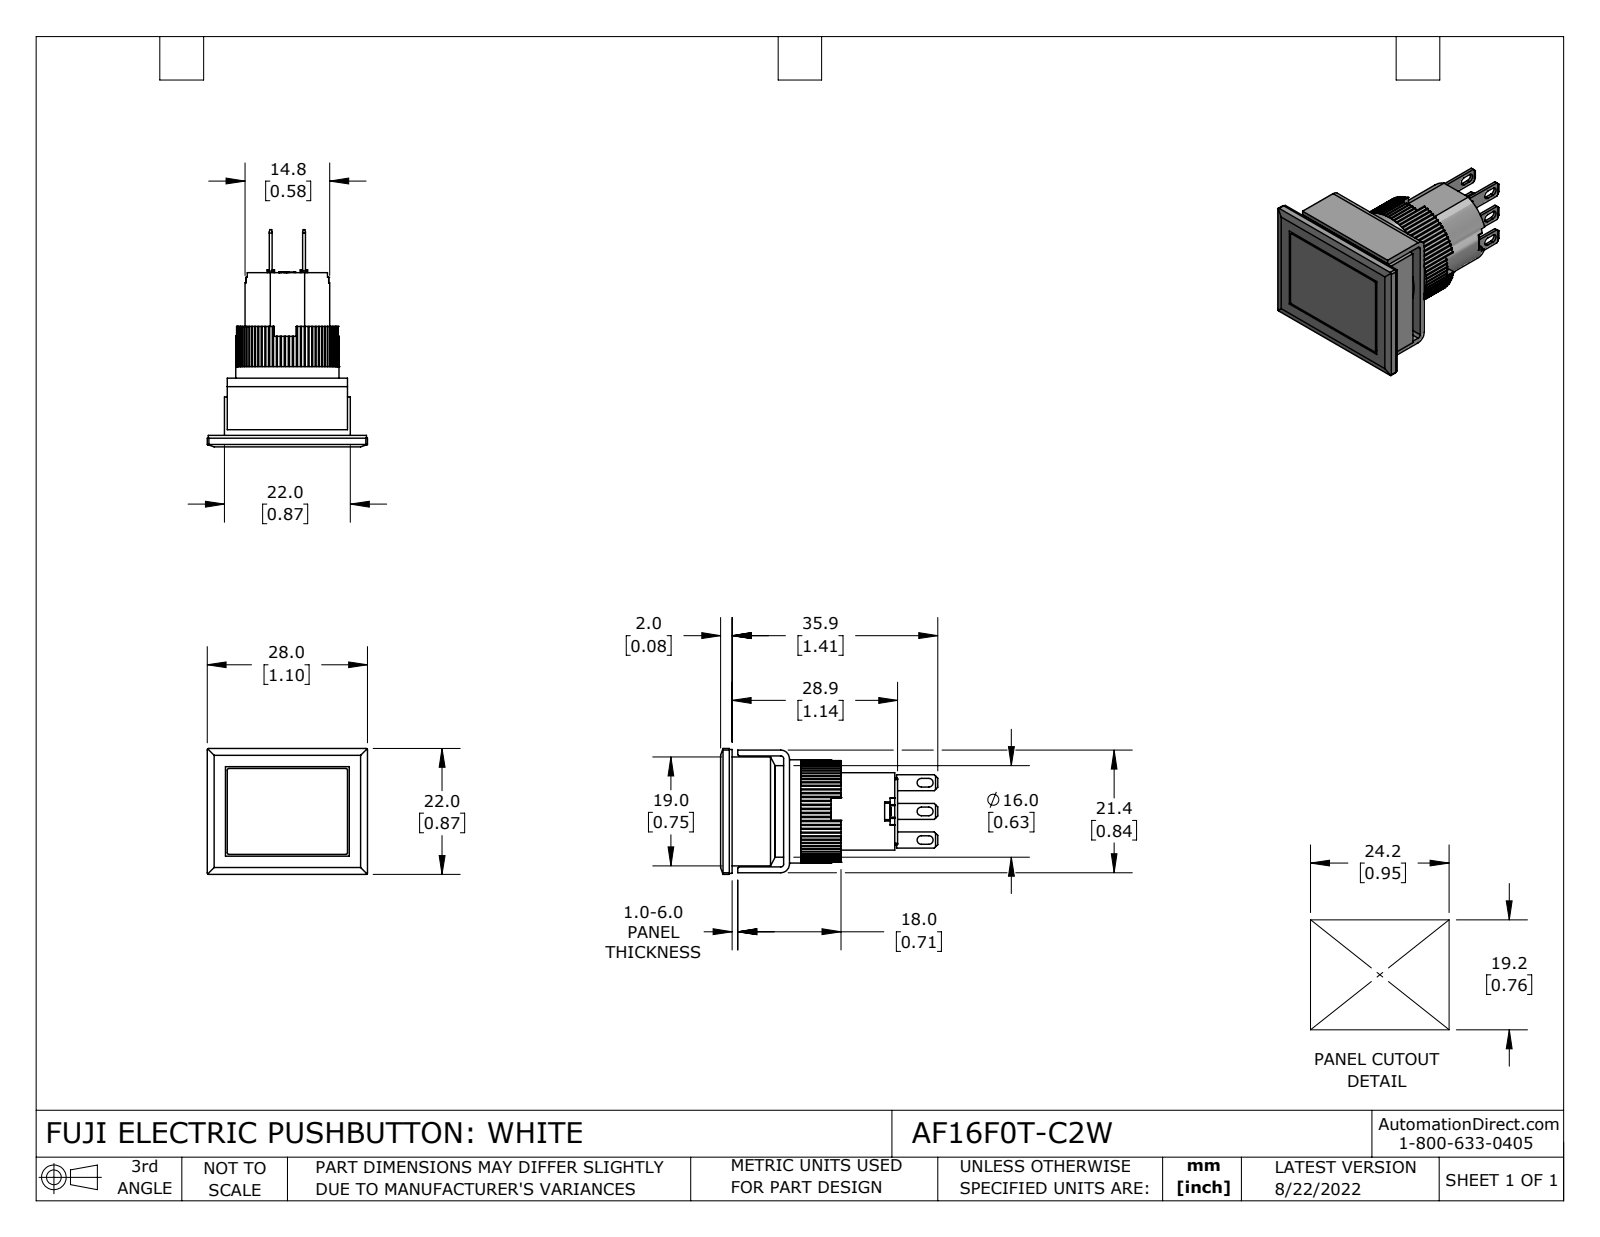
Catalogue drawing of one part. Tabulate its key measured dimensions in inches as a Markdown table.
| quantity | value |
| --- | --- |
| part name | AF16F0T-C2W |
| STEP written by | SolidWorks 2021 (CONFIG_CONTROL_DESIGN) |
| units | inches |
| bodies | 12 solids, 798 faces (620 planar, 176 cylindrical, 2 other) |
| overall size | 1.492 × 1.102 × 0.866 |
| volume | 0.541 in³ |
| surface area | 11.85 in² |
| round holes (diameter × count) | 0.039 × 1, 0.709 × 1 |
| round bosses / shafts (diameter × count) | 0.63 × 1, 0.583 × 1 |
| partial cylindrical surfaces (radius × count) | 0.01 × 80, 0.008 × 12, 0.012 × 8, 0.03 × 6, 0.02 × 2, 0.059 × 2 |
| main face-to-face distances | 0.374, 0.059, 0.02, 0.142, 0.039, 0.315, 0.232, 0.083, 0.079, 0.756 |
